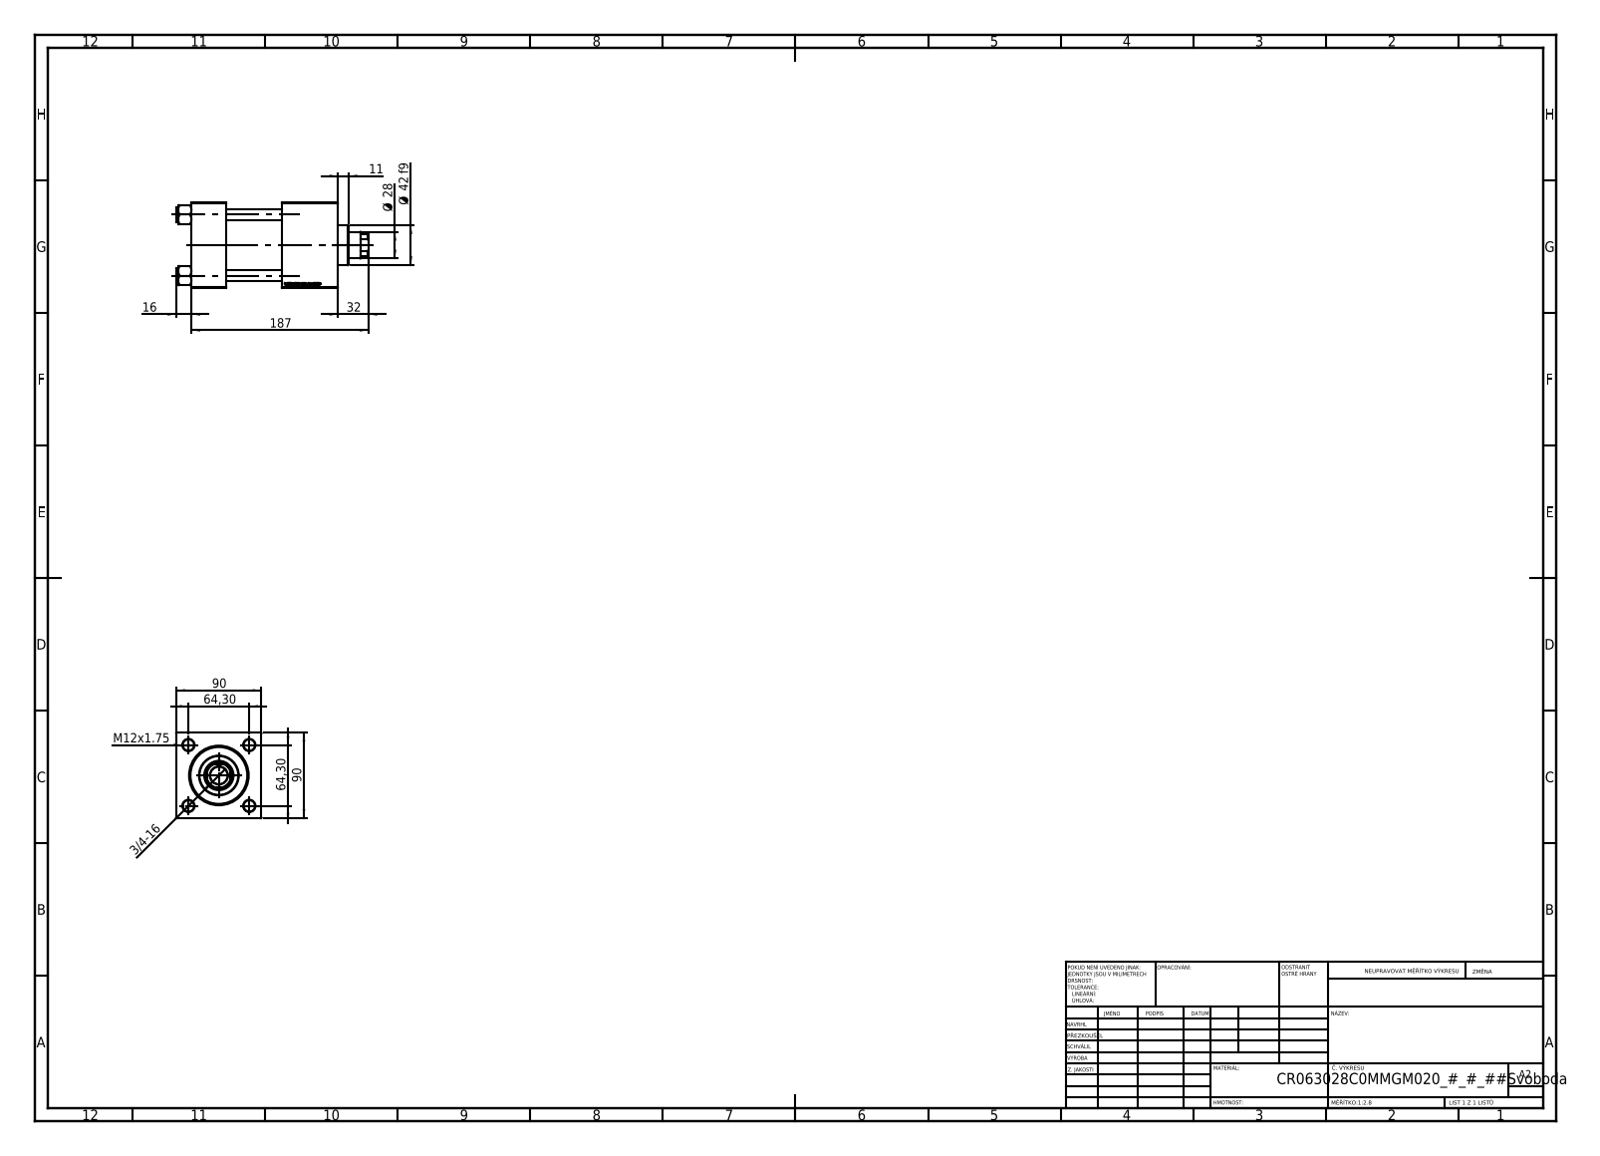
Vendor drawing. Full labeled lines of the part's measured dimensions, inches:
Part name (STEP PRODUCT): V215CR_C_TYCINKA; V215CR_C_Body; V215_VC_A; NUT_M5_C (+1 more)
STEP written by: SolidWorks 2019 (CONFIG_CONTROL_DESIGN)
Units: inches
Bodies: 11 solids, 1148 faces (526 planar, 86 cylindrical, 536 other)
Overall size (bounding box): 7.992 × 3.543 × 3.543
Volume: 57.81 in³ · Surface area: 277.5 in²
Round holes (diameter × count): ⌀0.472 ×4, ⌀0.276 ×2, ⌀0.825 ×2, ⌀1.181 ×2, ⌀0.728 ×1, ⌀1.102 ×1, ⌀1.22 ×1, ⌀1.969 ×1, ⌀2.362 ×1, ⌀2.48 ×1
Round bosses / shafts (diameter × count): ⌀0.591 ×4, ⌀2.717 ×1, ⌀1.654 ×1
Partial cylindrical surfaces — rounded edges, fillets, slot ends (radius × count): R0.531 ×1
Main face-to-face distances: 3.543, 2.323, 1.457, 6.102, 4.646, 3.78, 4.972, 3.516, 1.193, 1.13
Hole centre spacings: 1.79, 2.531, 3.58, 3.839
